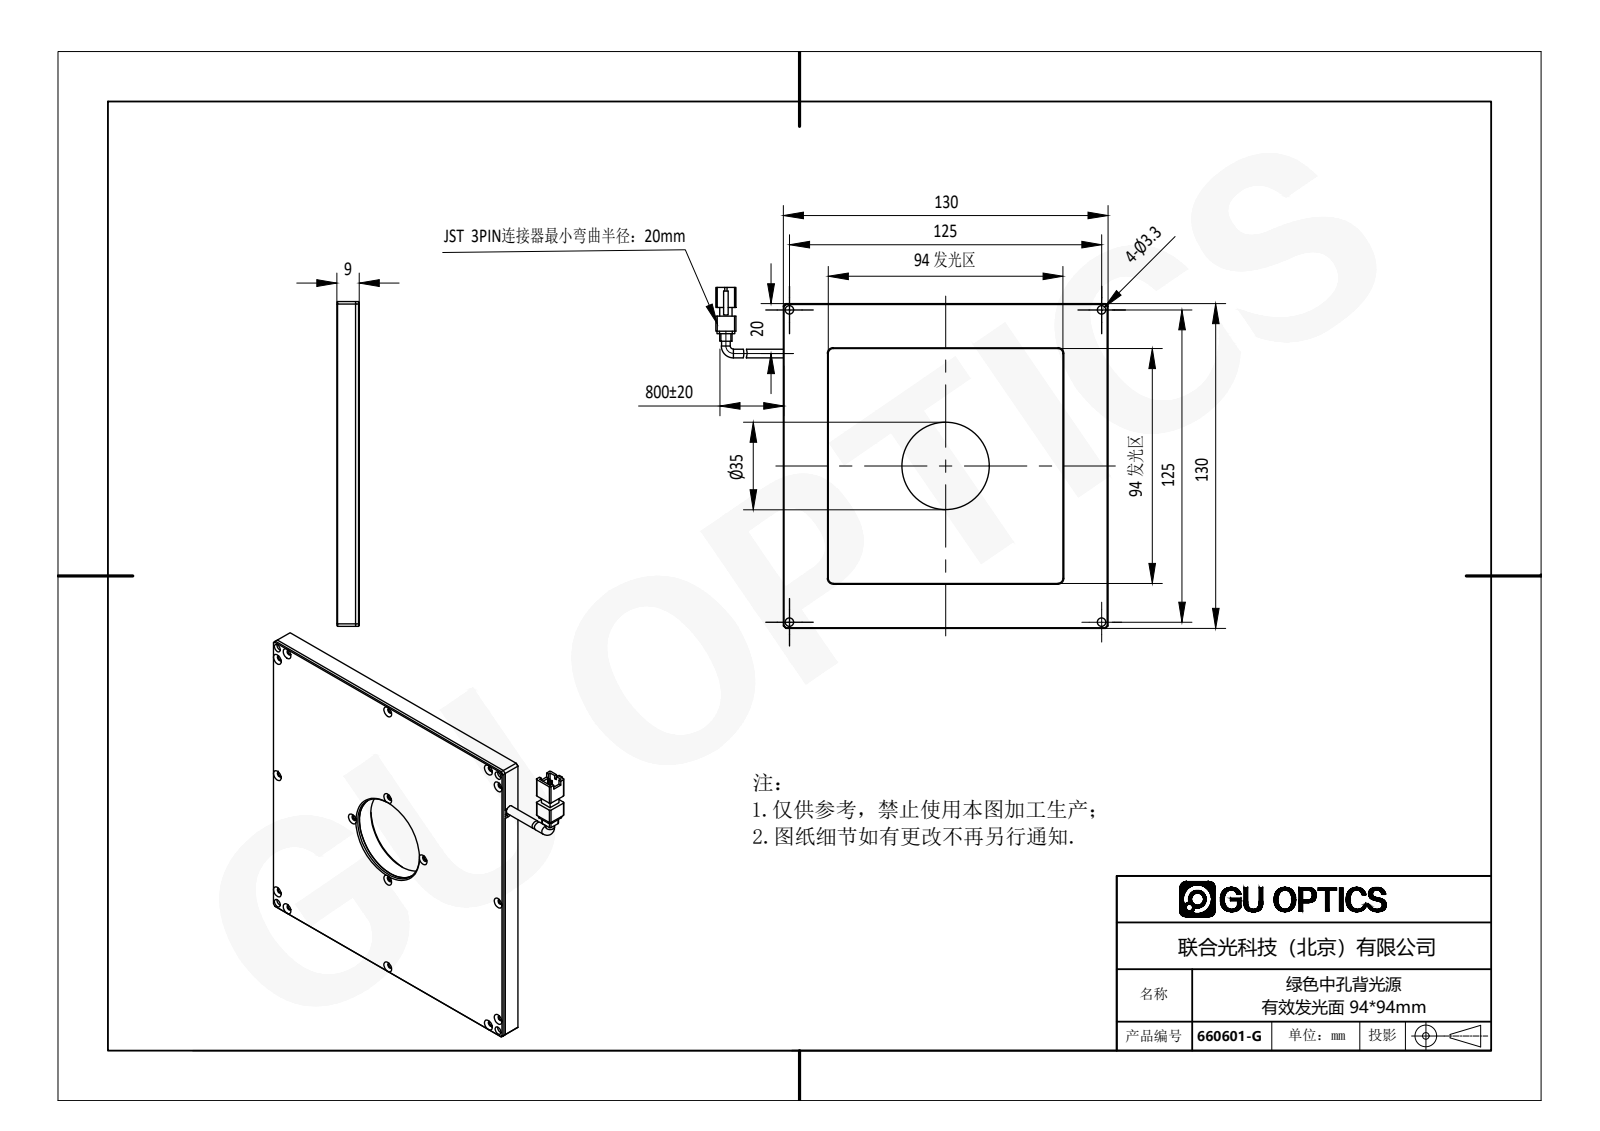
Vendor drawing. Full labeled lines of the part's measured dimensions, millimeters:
Part name (STEP PRODUCT): 660601-G
STEP written by: SolidWorks 2016 (AUTOMOTIVE_DESIGN)
Units: millimetres
Bodies: 6 solids, 474 faces (191 planar, 148 cylindrical, 135 other)
Overall size (bounding box): 157 × 136.5 × 10
Volume: 93 254 mm³ · Surface area: 85 777 mm²
Round holes (diameter × count): ⌀1.6 ×16, ⌀2 ×12, ⌀2.2 ×12, ⌀2.4 ×4, ⌀3.3 ×4, ⌀35 ×1, ⌀43 ×1
Round bosses / shafts (diameter × count): ⌀3.5 ×2, ⌀45.8 ×1, ⌀42.8 ×1
Partial cylindrical surfaces — rounded edges, fillets, slot ends (radius × count): R0.5 ×8, R1.5 ×6, R1 ×4, R2 ×4, R1.6 ×1
Main face-to-face distances: 4, 6.5, 1.5, 8, 2.5, 9, 5, 1, 7.5, 126
Hole centre spacings: 62.5, 125, 5.5, 57, 62.74, 65.62, 71.1, 72.63
